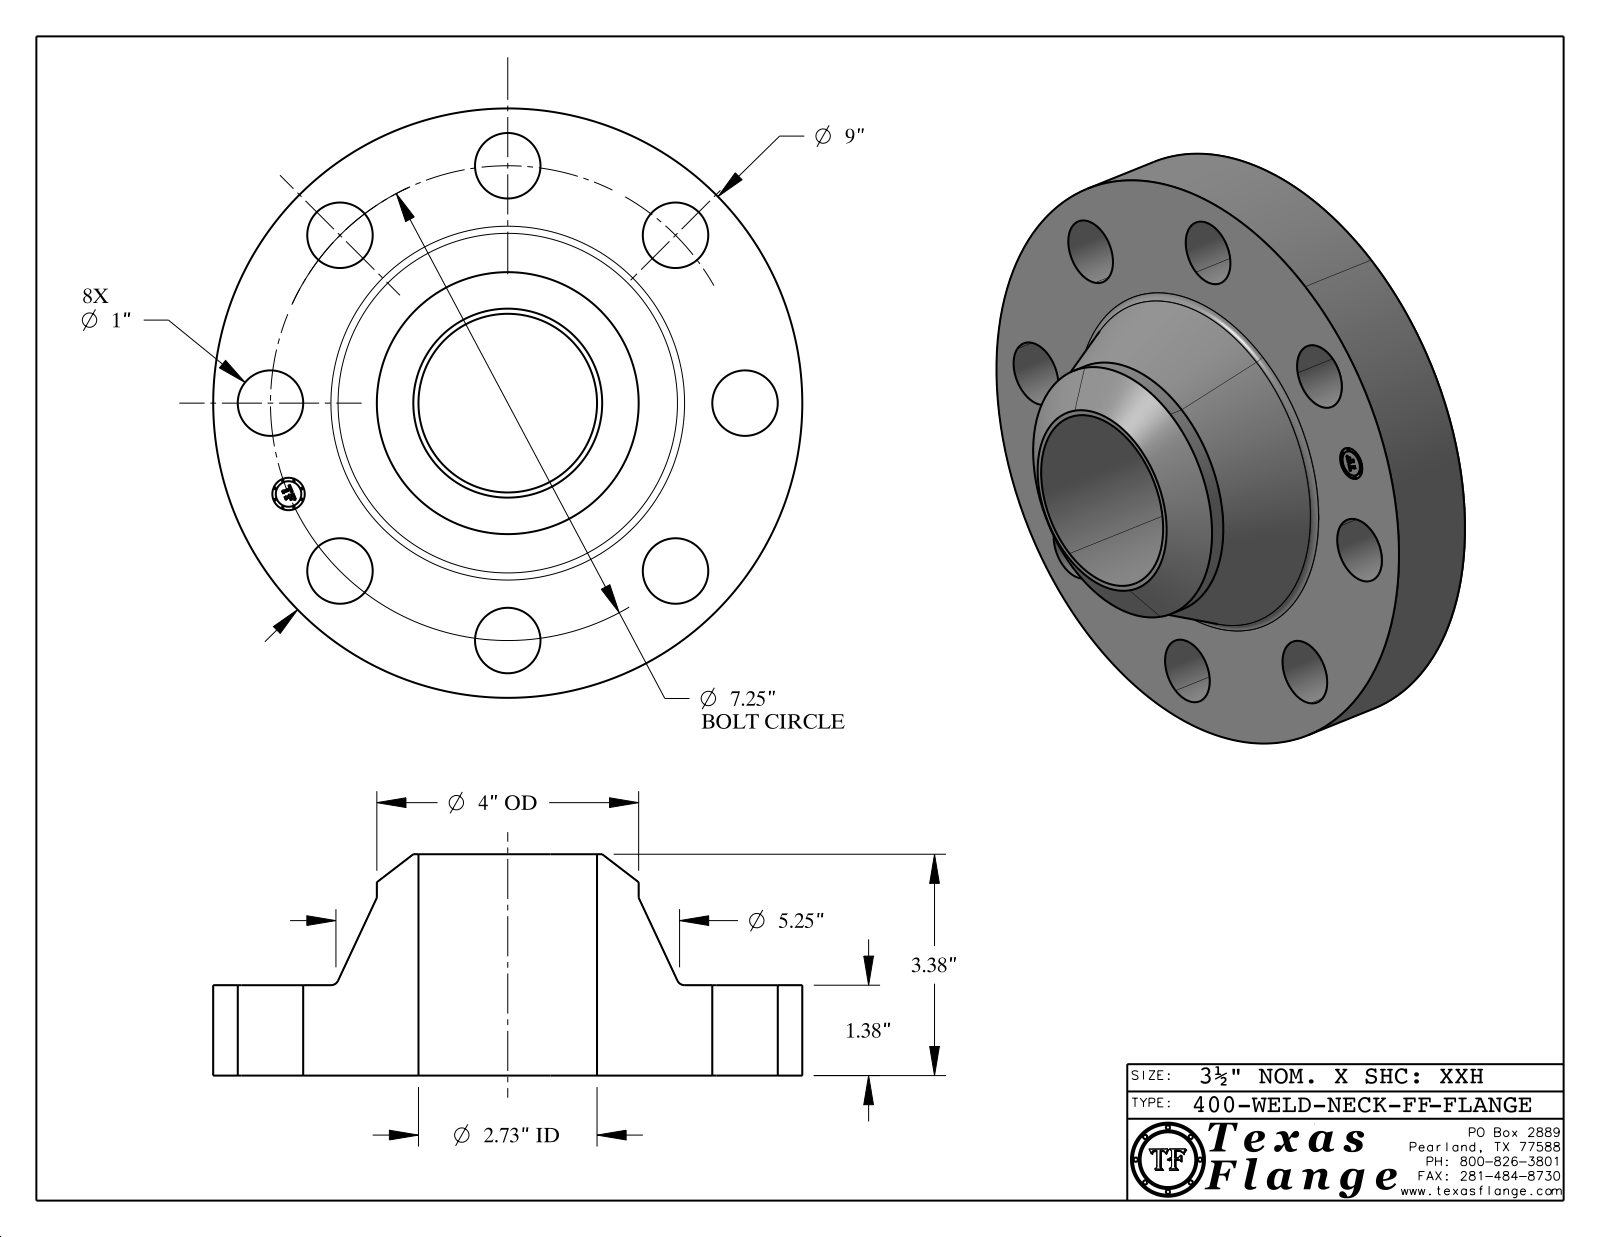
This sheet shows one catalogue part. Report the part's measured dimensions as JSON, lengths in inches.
{"part_name": "400-WELD-NECK-FF", "step_written_by": "CATIA V5 STEP AP214 (AUTOMOTIVE_DESIGN)", "units": "inches", "bodies": {"solids": 1, "faces": 416, "planar": 368, "cylindrical": 42, "other": 6}, "overall_size": [9, 9, 3.38], "volume_in3": 88.95, "surface_area_in2": 222.4, "round_holes": [[1, 8], [0.495, 1], [2.728, 1]], "round_bosses_or_shafts": [[0.03, 8], [9, 1], [4, 1], [0.39, 1]], "face_to_face_distances": [1.38, 3.38, 2, 1.365, 0.015, 2.015, 0.148, 0.144, 0.027, 0.096], "hole_center_spacings": [3.625, 2.774, 5.127, 6.698, 7.25, 1.415, 7.111, 4.028]}
